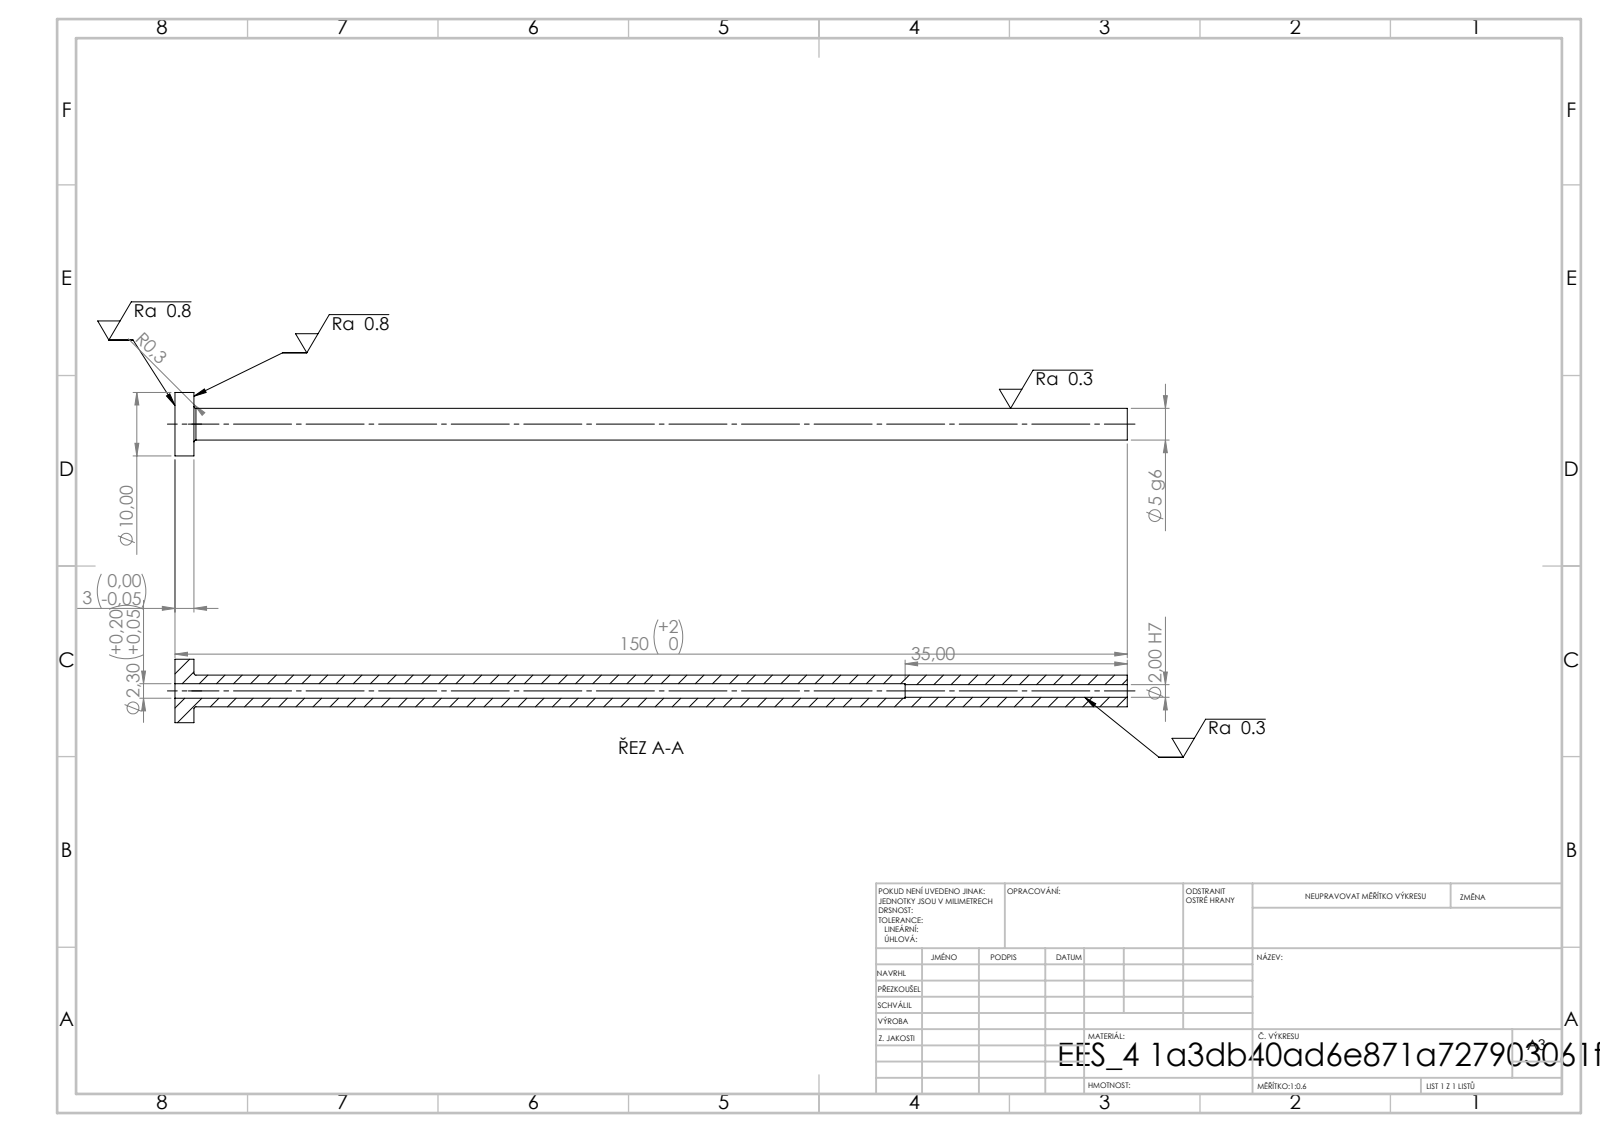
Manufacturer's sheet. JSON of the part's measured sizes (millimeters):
{"step_written_by": "SolidWorks 2019 (CONFIG_CONTROL_DESIGN)", "units": "millimeters", "bodies": {"solids": 1, "faces": 14, "planar": 4, "cylindrical": 8, "other": 2}, "overall_size": [150, 10, 10], "volume_mm3": 2535, "surface_area_mm2": 3603, "round_holes": [[2, 1], [2.3, 1]], "round_bosses_or_shafts": [[10, 1], [5, 1]], "face_to_face_distances": [3, 150, 147, 115, 112, 35]}
